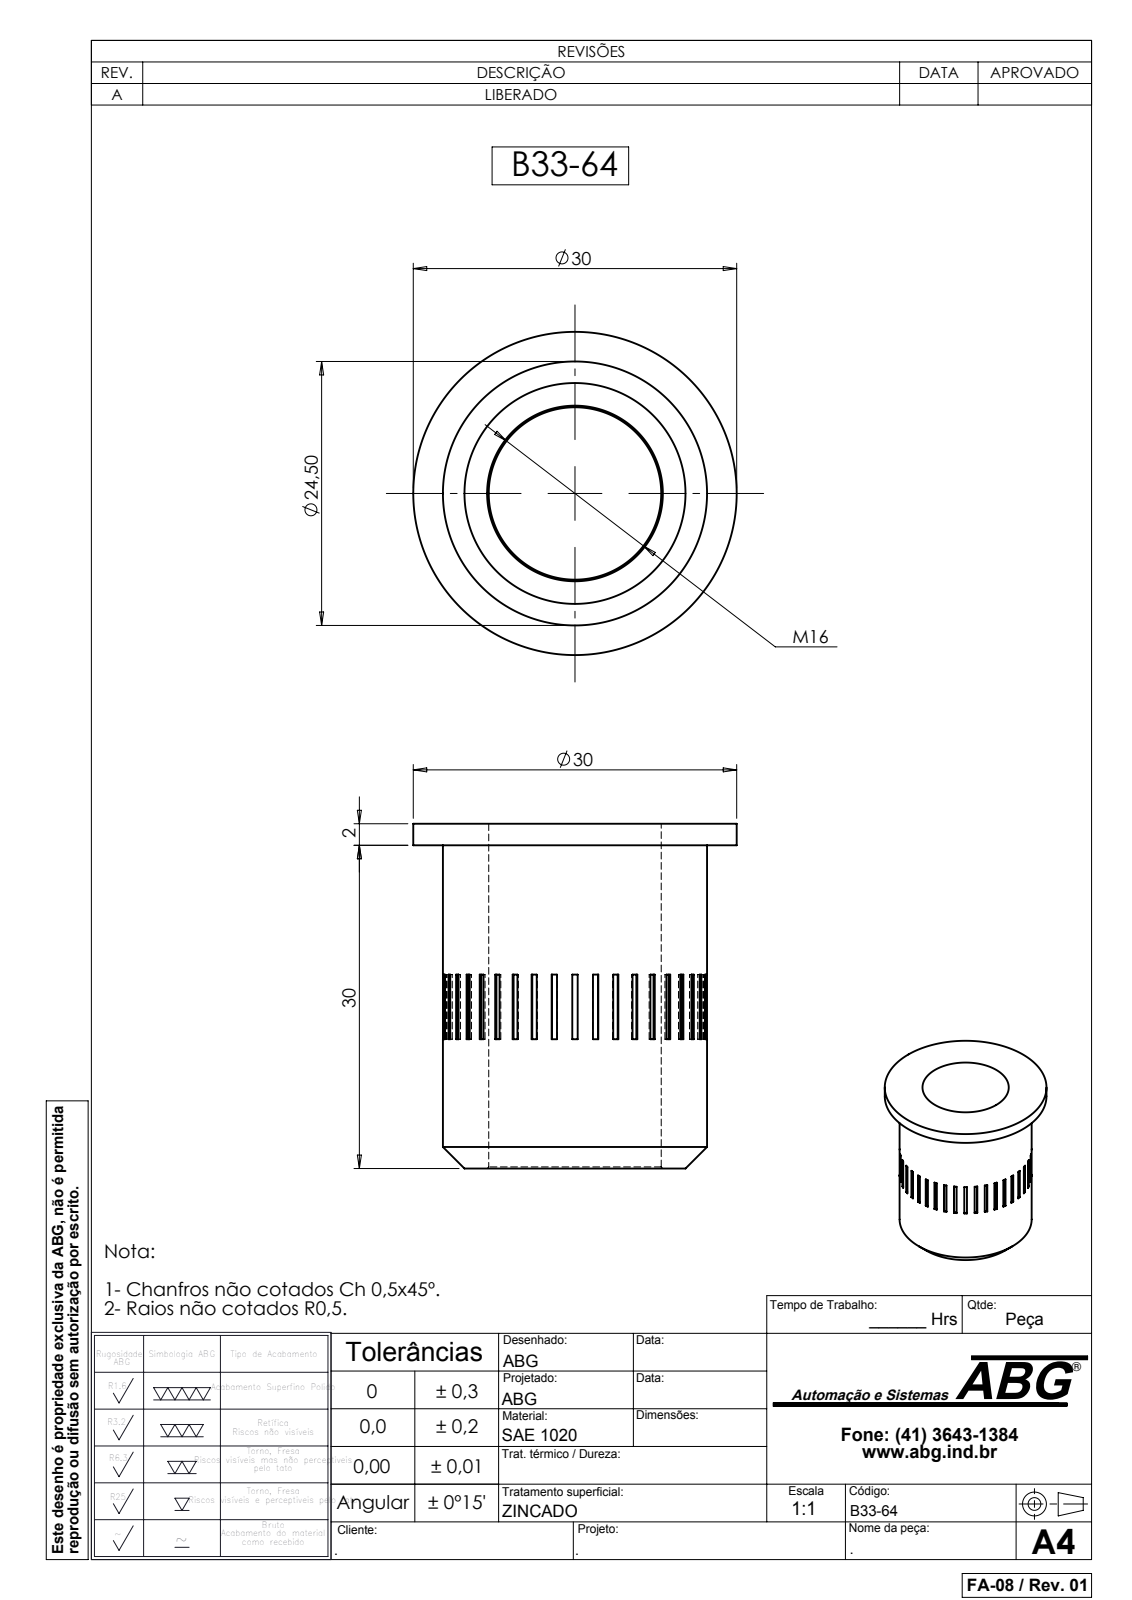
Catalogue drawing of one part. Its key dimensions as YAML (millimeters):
part_name: "B33-64"
step_written_by: "SolidWorks 2007 (CONFIG_CONTROL_DESIGN)"
units: millimeters
bodies: {solids: 1, faces: 213, planar: 203, cylindrical: 6, other: 4}
overall_size: [32, 30, 30]
volume: 8953
surface_area: 5121
round_holes:
  - {diameter: 16, count: 1}
round_bosses_or_shafts:
  - {diameter: 30, count: 1}
  - {diameter: 24.5, count: 1}
face_to_face_distances: [2, 30, 32, 12.3, 11.8, 24.1, 0.5, 11.79, 12.31, 12.29]
